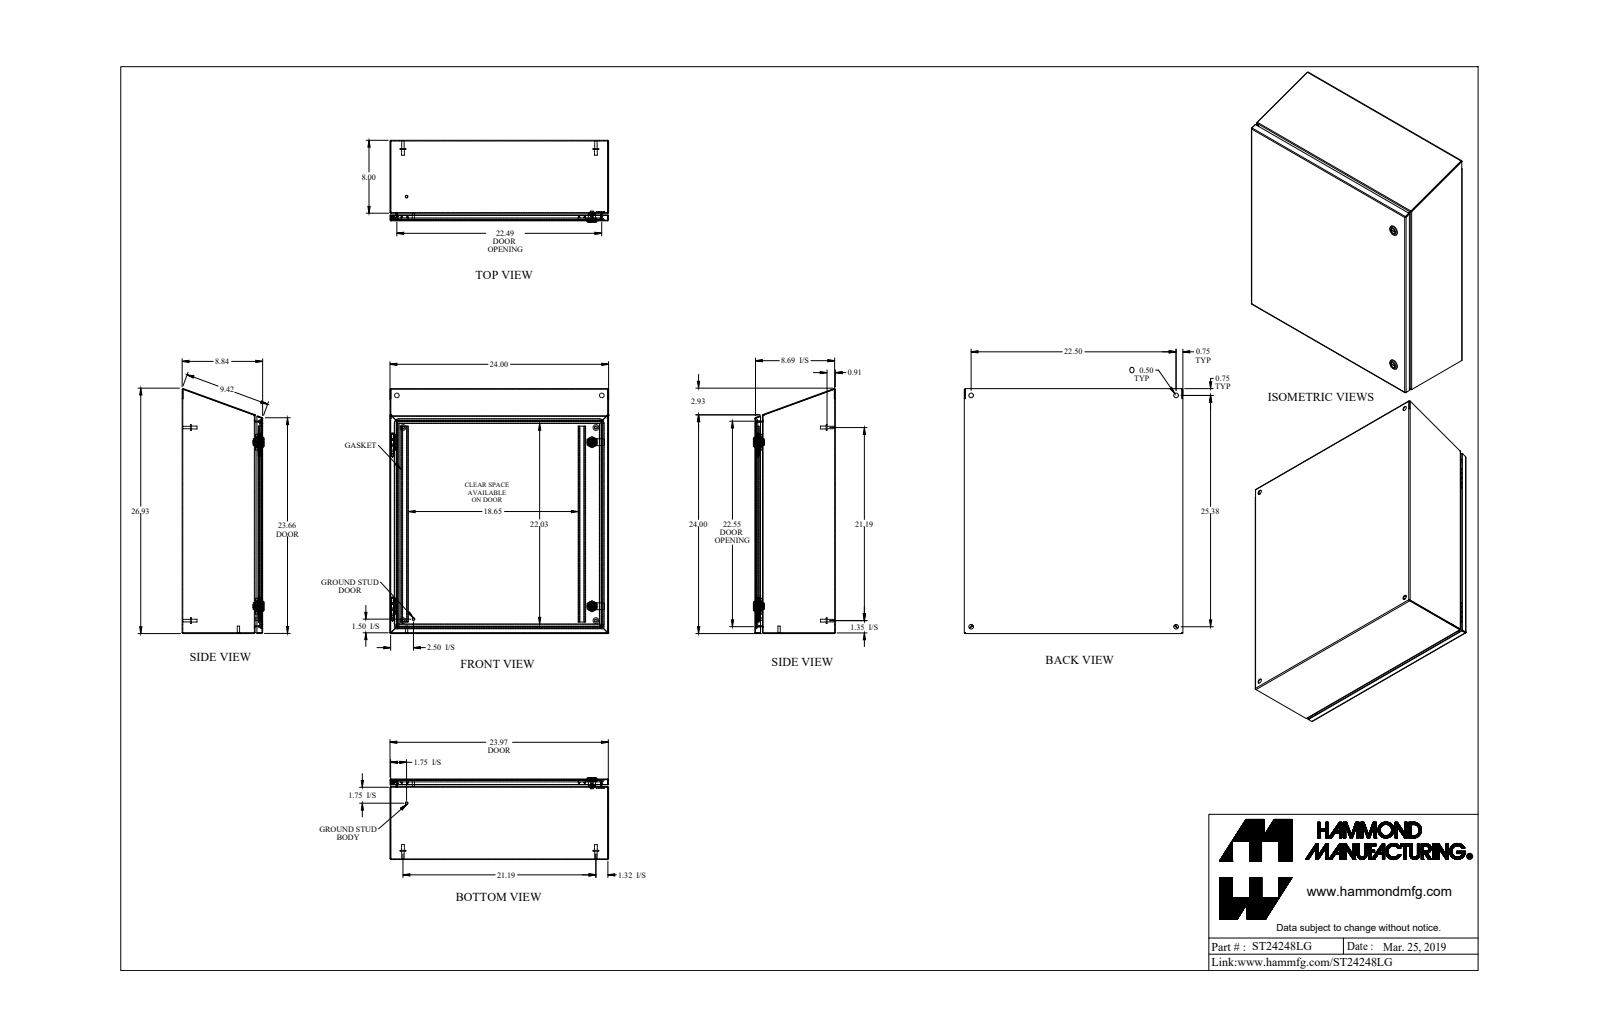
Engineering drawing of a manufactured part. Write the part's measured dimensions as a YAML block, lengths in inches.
part_name: "ST24248LG"
step_written_by: "SolidWorks 2018 (AUTOMOTIVE_DESIGN)"
units: inches
bodies: {solids: 27, faces: 789, planar: 416, cylindrical: 241, other: 132}
overall_size: [26.88, 24, 8.997]
volume: 170.9
surface_area: 4784
round_holes:
  - {diameter: 0.5, count: 4}
  - {diameter: 0.232, count: 2}
  - {diameter: 0.625, count: 2}
  - {diameter: 0.785, count: 2}
  - {diameter: 0.172, count: 1}
  - {diameter: 0.24, count: 1}
  - {diameter: 0.242, count: 1}
round_bosses_or_shafts:
  - {diameter: 0.625, count: 4}
  - {diameter: 0.313, count: 4}
  - {diameter: 0.27, count: 4}
  - {diameter: 1.1, count: 2}
  - {diameter: 0.525, count: 2}
  - {diameter: 0.281, count: 2}
  - {diameter: 0.25, count: 2}
  - {diameter: 0.455, count: 1}
partial_cylinders:
  - {radius: 0.036, count: 20}
  - {radius: 0.108, count: 20}
  - {radius: 0.043, count: 12}
  - {radius: 0.081, count: 12}
  - {radius: 0.25, count: 11}
  - {radius: 0.006, count: 4}
  - {radius: 0.062, count: 4}
  - {radius: 0.125, count: 4}
face_to_face_distances: [0.072, 8.765, 8.693, 8.837, 23.928, 23.856, 24, 7.928, 0.837, 0.909]
hole_center_spacings: [22.5, 25.38, 33.917, 2.493, 5.241, 18, 20.278, 21.544]
